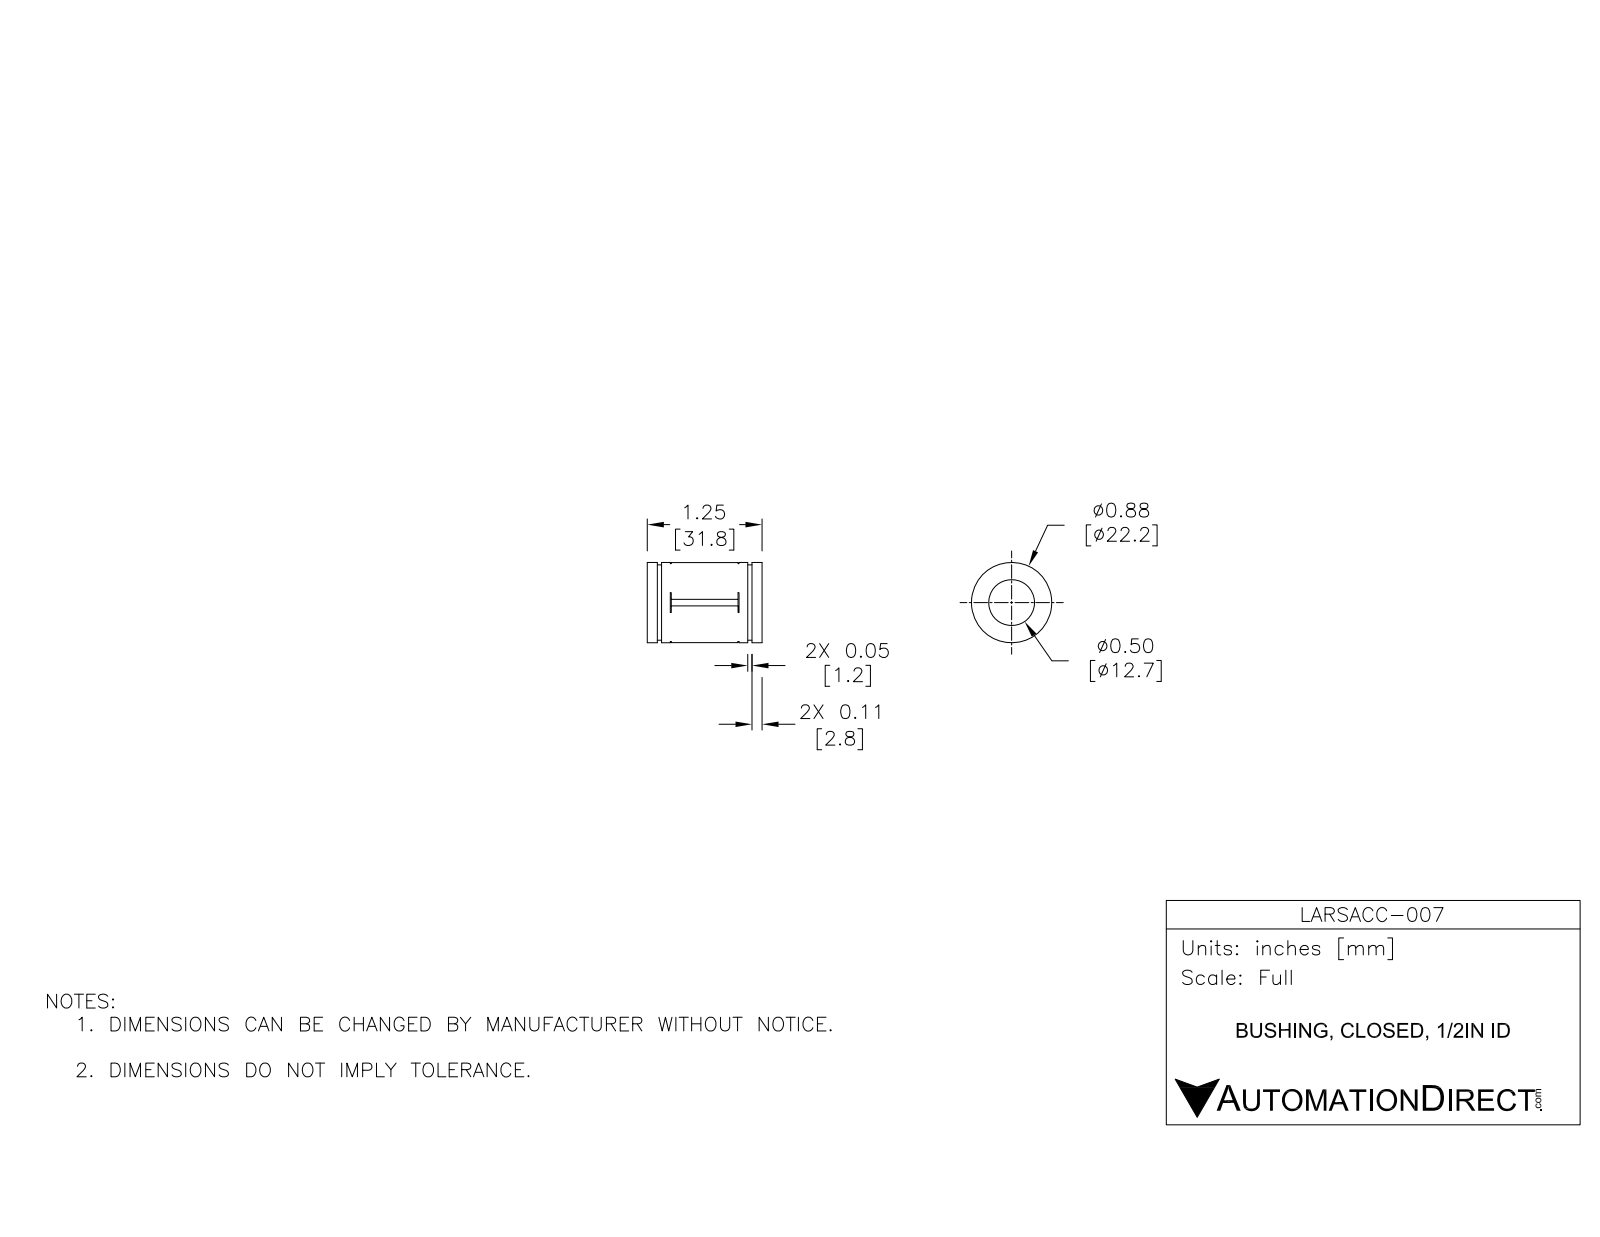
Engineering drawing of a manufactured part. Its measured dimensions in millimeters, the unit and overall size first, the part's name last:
Units: millimetres
Overall size (bounding box): 31.8 × 22.2 × 22.2
Round holes (diameter × count): ⌀12.7 ×1
Round bosses / shafts (diameter × count): ⌀22.2 ×1, ⌀20.9 ×1
Partial cylindrical surfaces — rounded edges, fillets, slot ends (radius × count): R11.5 ×4
Main face-to-face distances: 31.8, 2.8, 29, 3.9, 27.8, 1.2, 25, 22.1, 23.9, 26.2
Volume: 8 180 mm³ · Surface area: 4 223 mm²
Bodies: 1 solid, 48 faces (26 planar, 22 cylindrical, 0 other)
Part name (STEP PRODUCT): LARSACC-007
STEP written by: SolidWorks 2015 (AUTOMOTIVE_DESIGN)
